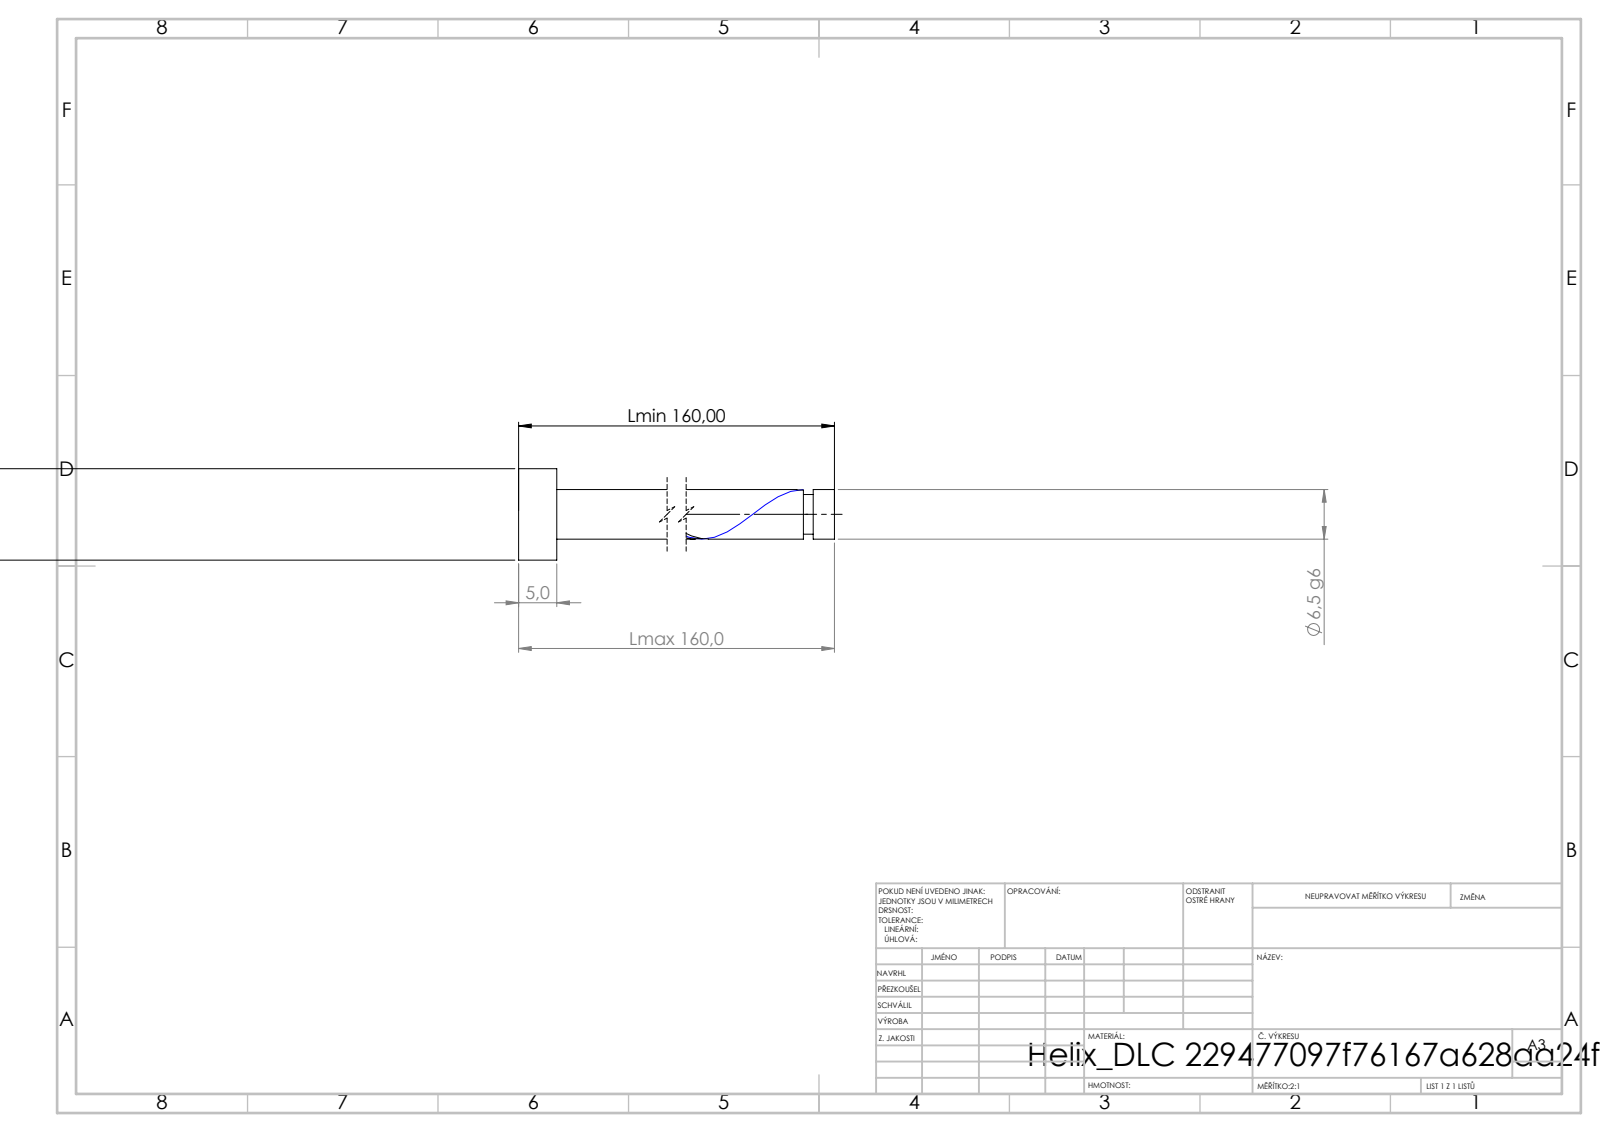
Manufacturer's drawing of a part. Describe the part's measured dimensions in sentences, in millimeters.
Its 3-D file was written by "SolidWorks 2019 (CONFIG_CONTROL_DESIGN)". It is 1 solid with 21 faces: 6 planar, 14 cylindrical and 1 other. Overall it measures 160 by 12 by 12 millimeters. Its volume is 5 642 cubic millimeters and its surface area 3 666 square millimeters. Round bosses or shafts: 1 of diameter 12, 1 of diameter 6.5, 1 of diameter 5.2. The main face-to-face distances are 5, 160, 155, 157.22, 152.22, 2.78, 155.92, 150.92, 1.3, 4.08.
